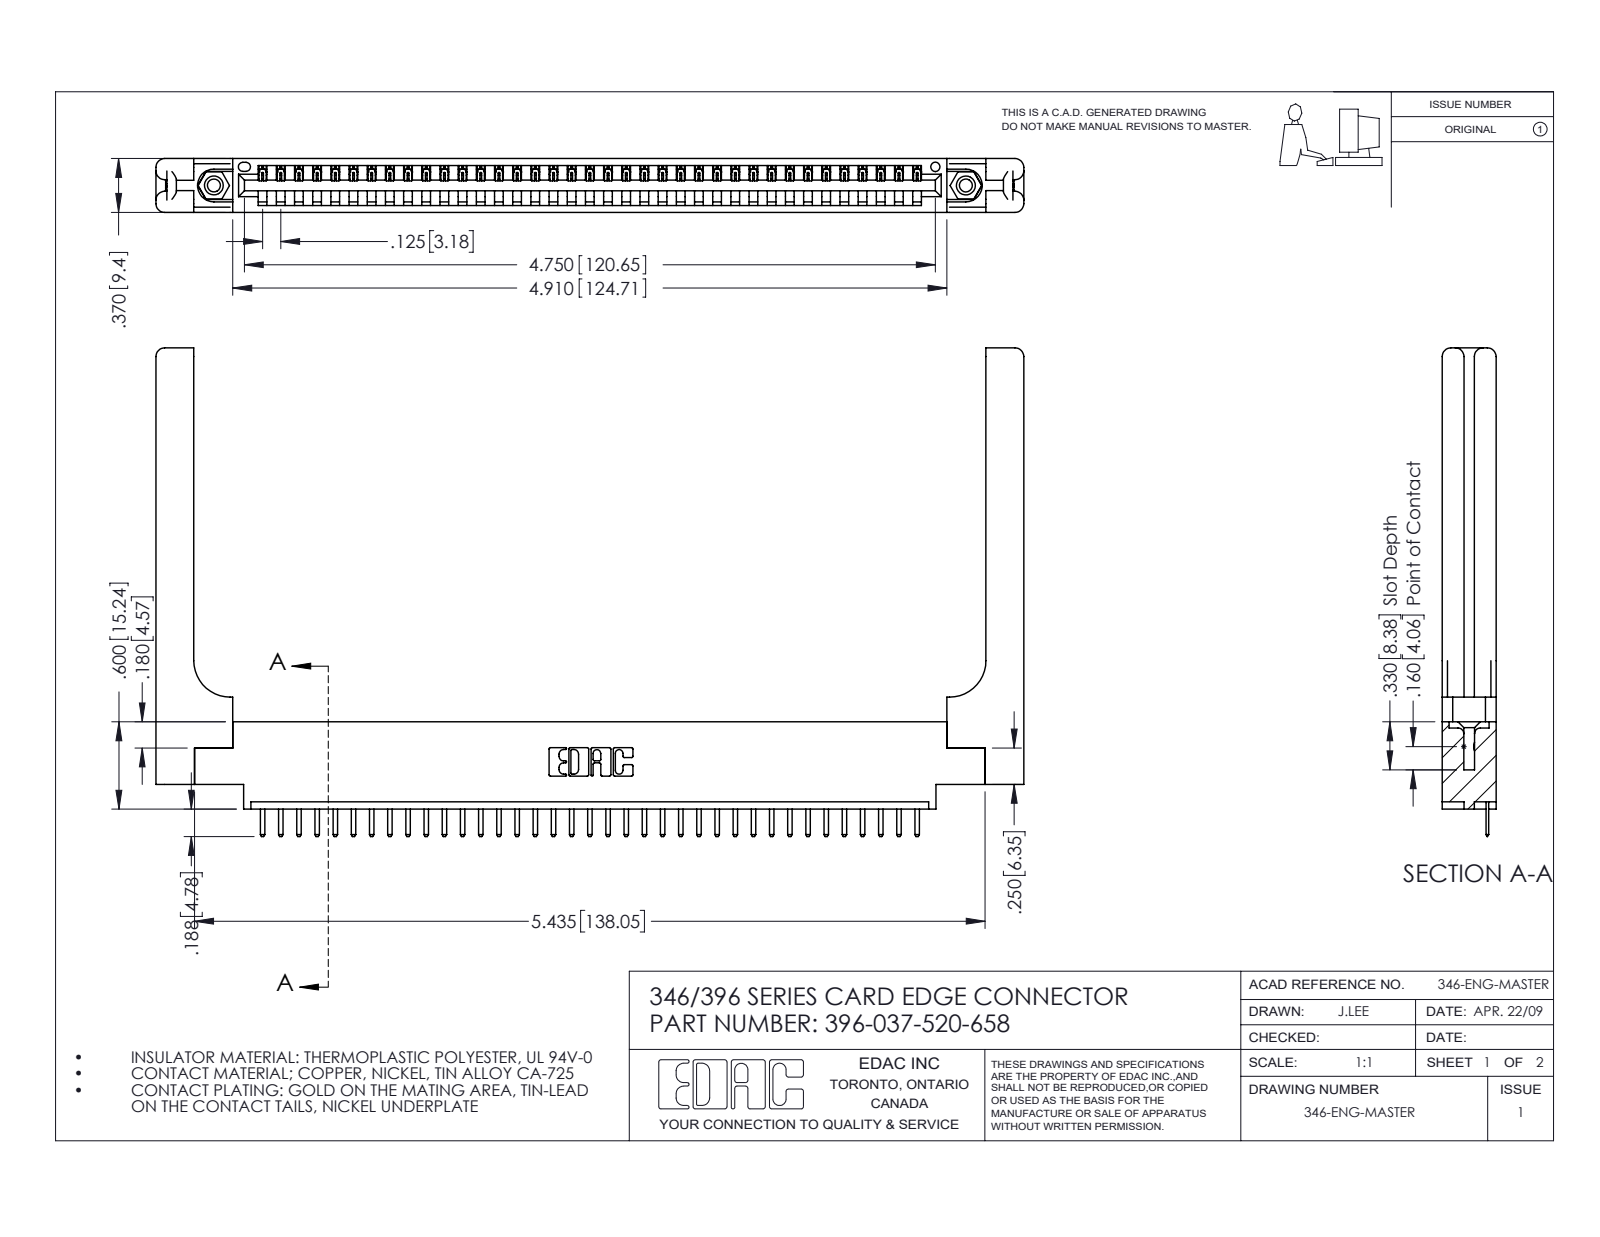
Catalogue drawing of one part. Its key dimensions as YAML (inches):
part_name: "396-037-520-658; 346-220-058_345-220-058; 346 Part_0.170 Offset - 0.156 Dia-TH; 345-292-001_345-293-120 (+1 more)"
step_written_by: "SolidWorks 2016 (CONFIG_CONTROL_DESIGN)"
units: inches
bodies: {solids: 42, faces: 2676, planar: 1782, cylindrical: 834, other: 60}
overall_size: [5.966, 3.358, 0.37]
volume: 1.326
surface_area: 35.16
round_holes:
  - {diameter: 0.089, count: 2}
  - {diameter: 0.125, count: 2}
  - {diameter: 0.156, count: 2}
  - {diameter: 0.064, count: 1}
round_bosses_or_shafts:
  - {diameter: 0.155, count: 2}
partial_cylinders:
  - {radius: 0.01, count: 76}
  - {radius: 0.006, count: 74}
  - {radius: 0.01, count: 22}
  - {radius: 0.06, count: 16}
  - {radius: 0.007, count: 6}
  - {radius: 0.031, count: 6}
  - {radius: 0.026, count: 3}
  - {radius: 0.03, count: 2}
face_to_face_distances: [0.37, 0.048, 0.322, 0.072, 0.148, 0.15, 0.25, 0.298, 0.025, 0.222]
hole_center_spacings: [0.246, 4.961, 5.17]
